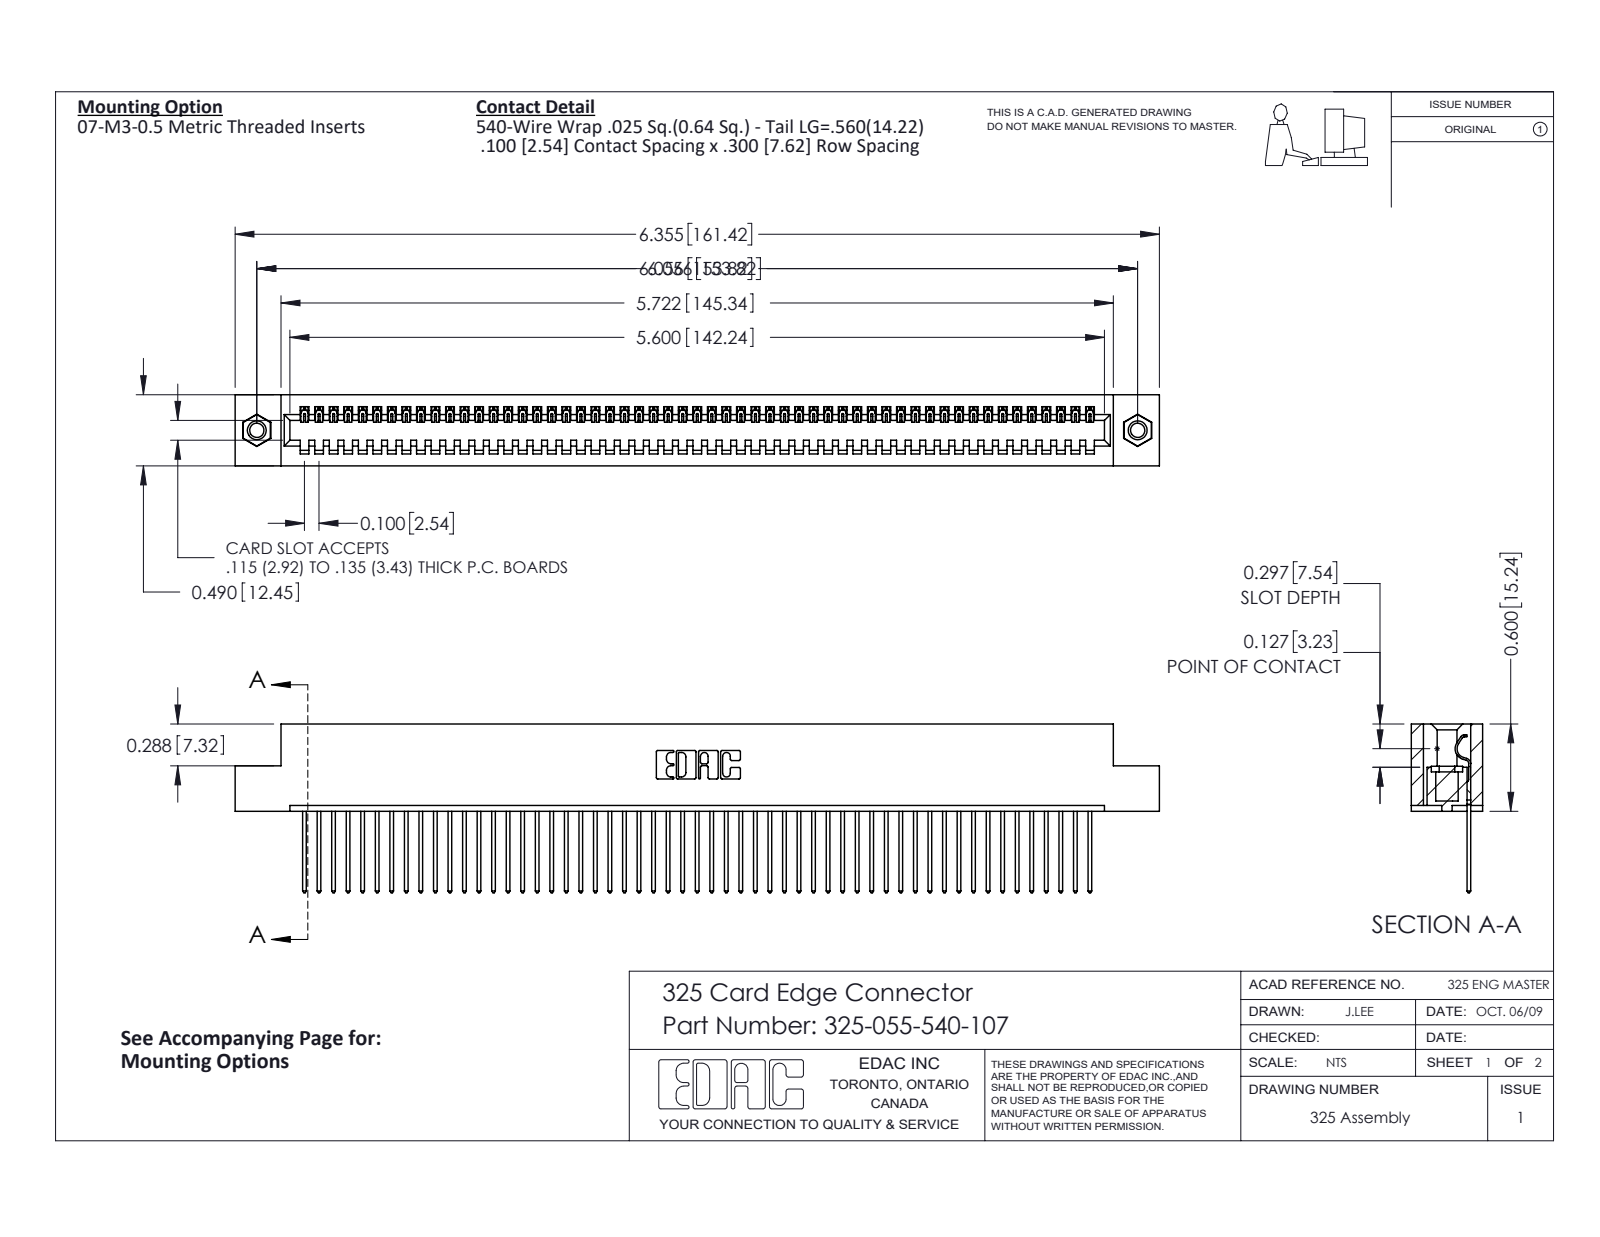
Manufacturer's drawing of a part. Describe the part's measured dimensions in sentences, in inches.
The part is named "345-250-001_345-250-005-103; 325-292-001_325-293-140; 325 Part_TI; 325-055-540-107". Its 3-D file was written by "SolidWorks 2016 (CONFIG_CONTROL_DESIGN)". It is 58 solids with 3364 faces: 2412 planar, 936 cylindrical and 16 other. Overall it measures 6.355 by 1.16 by 0.49 inches. Its volume is 1.26 cubic inches and its surface area 36.22 square inches. Round holes: 2 of diameter 0.098, 2 of diameter 0.125, 2 of diameter 0.16. Round bosses or shafts: 2 of diameter 0.155. Partial cylindrical surfaces (rounded edges, fillets, slot ends): 110 of radius 0.006, 110 of radius 0.01, 22 of radius 0.01, 6 of radius 0.007, 6 of radius 0.031, 3 of radius 0.026, 1 of radius 0.014, 1 of radius 0.022. The main face-to-face distances are 0.083, 0.407, 0.49, 0.107, 0.383, 0.025, 0.3, 0.325, 0.56, 0.263. The hole center spacings are 6.056.
